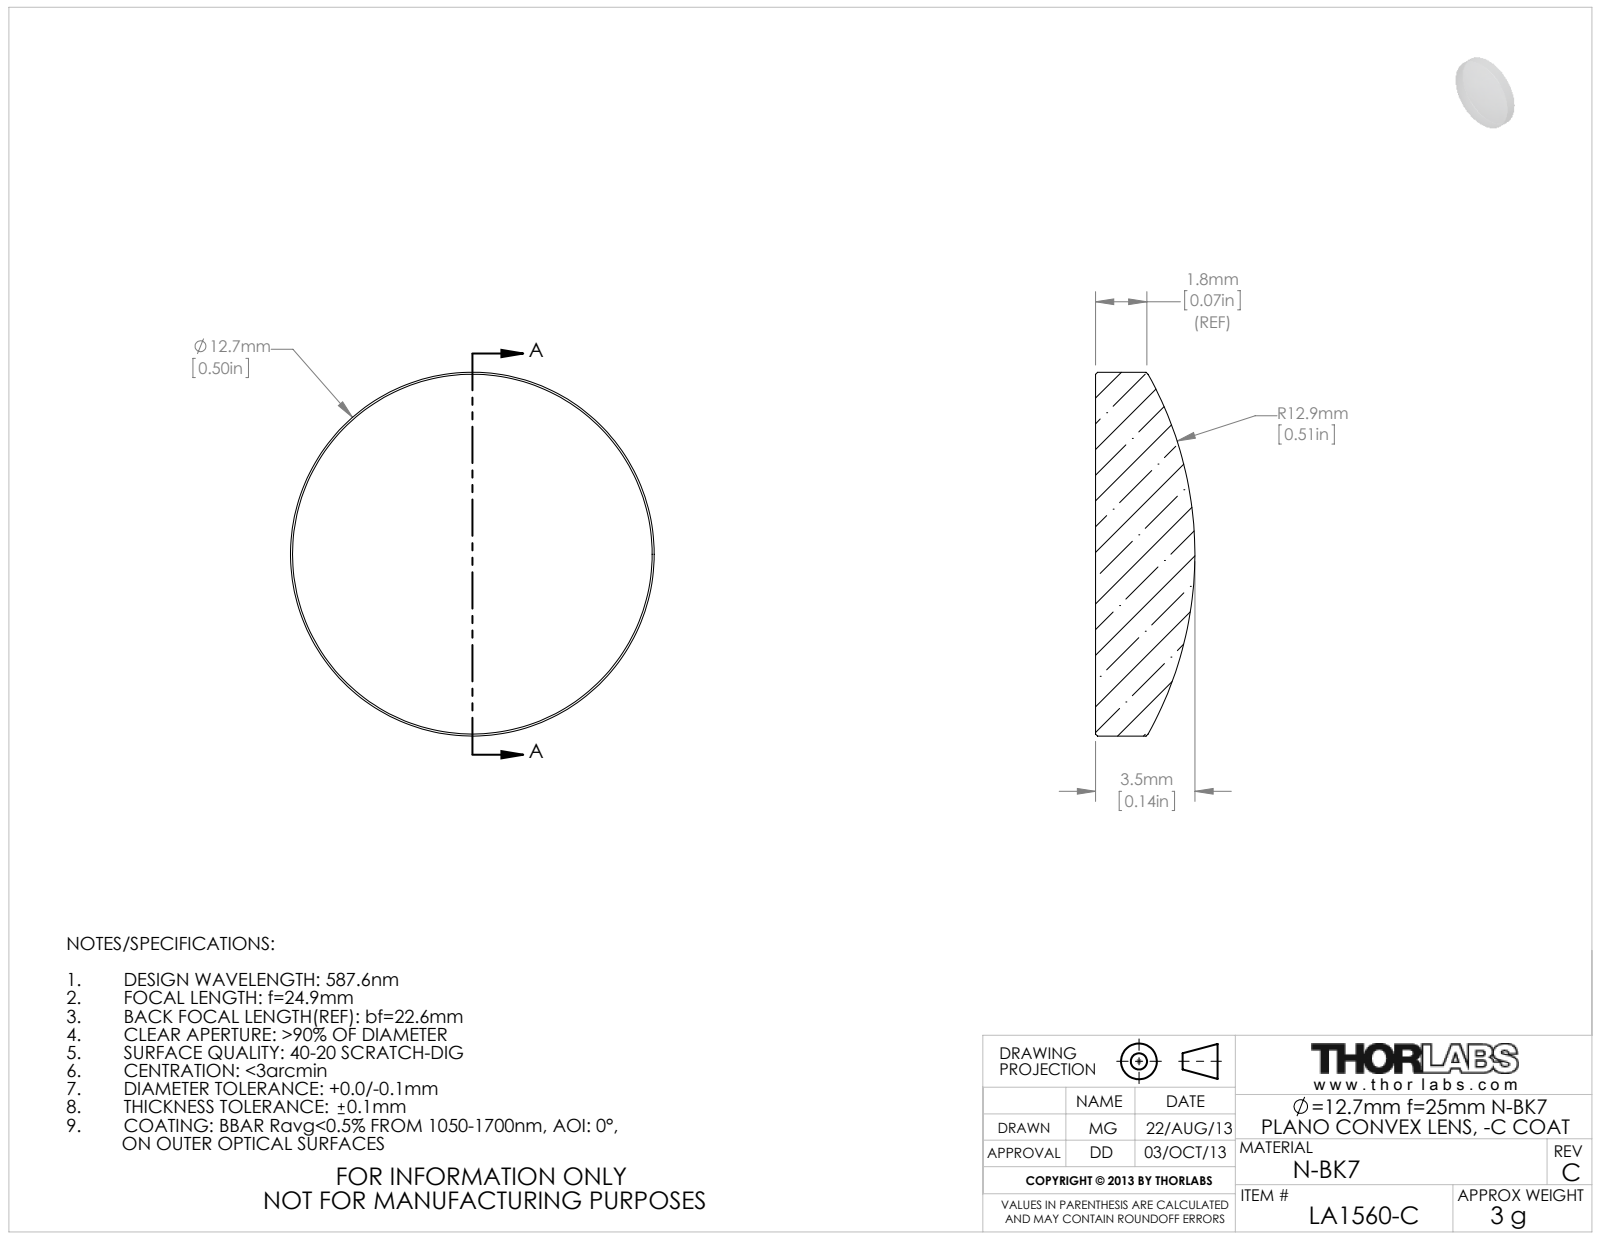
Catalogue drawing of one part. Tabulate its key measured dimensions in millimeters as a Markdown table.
| quantity | value |
| --- | --- |
| part name | 4554-E0W |
| STEP written by | SolidWorks 2009 (AUTOMOTIVE_DESIGN) |
| units | millimeters |
| bodies | 1 solid, 5 faces (1 planar, 2 cylindrical, 2 other) |
| overall size | 12.7 × 12.7 × 3.47 |
| volume | 336 mm³ |
| surface area | 334 mm² |
| round bosses / shafts (diameter × count) | 12.7 × 1 |
